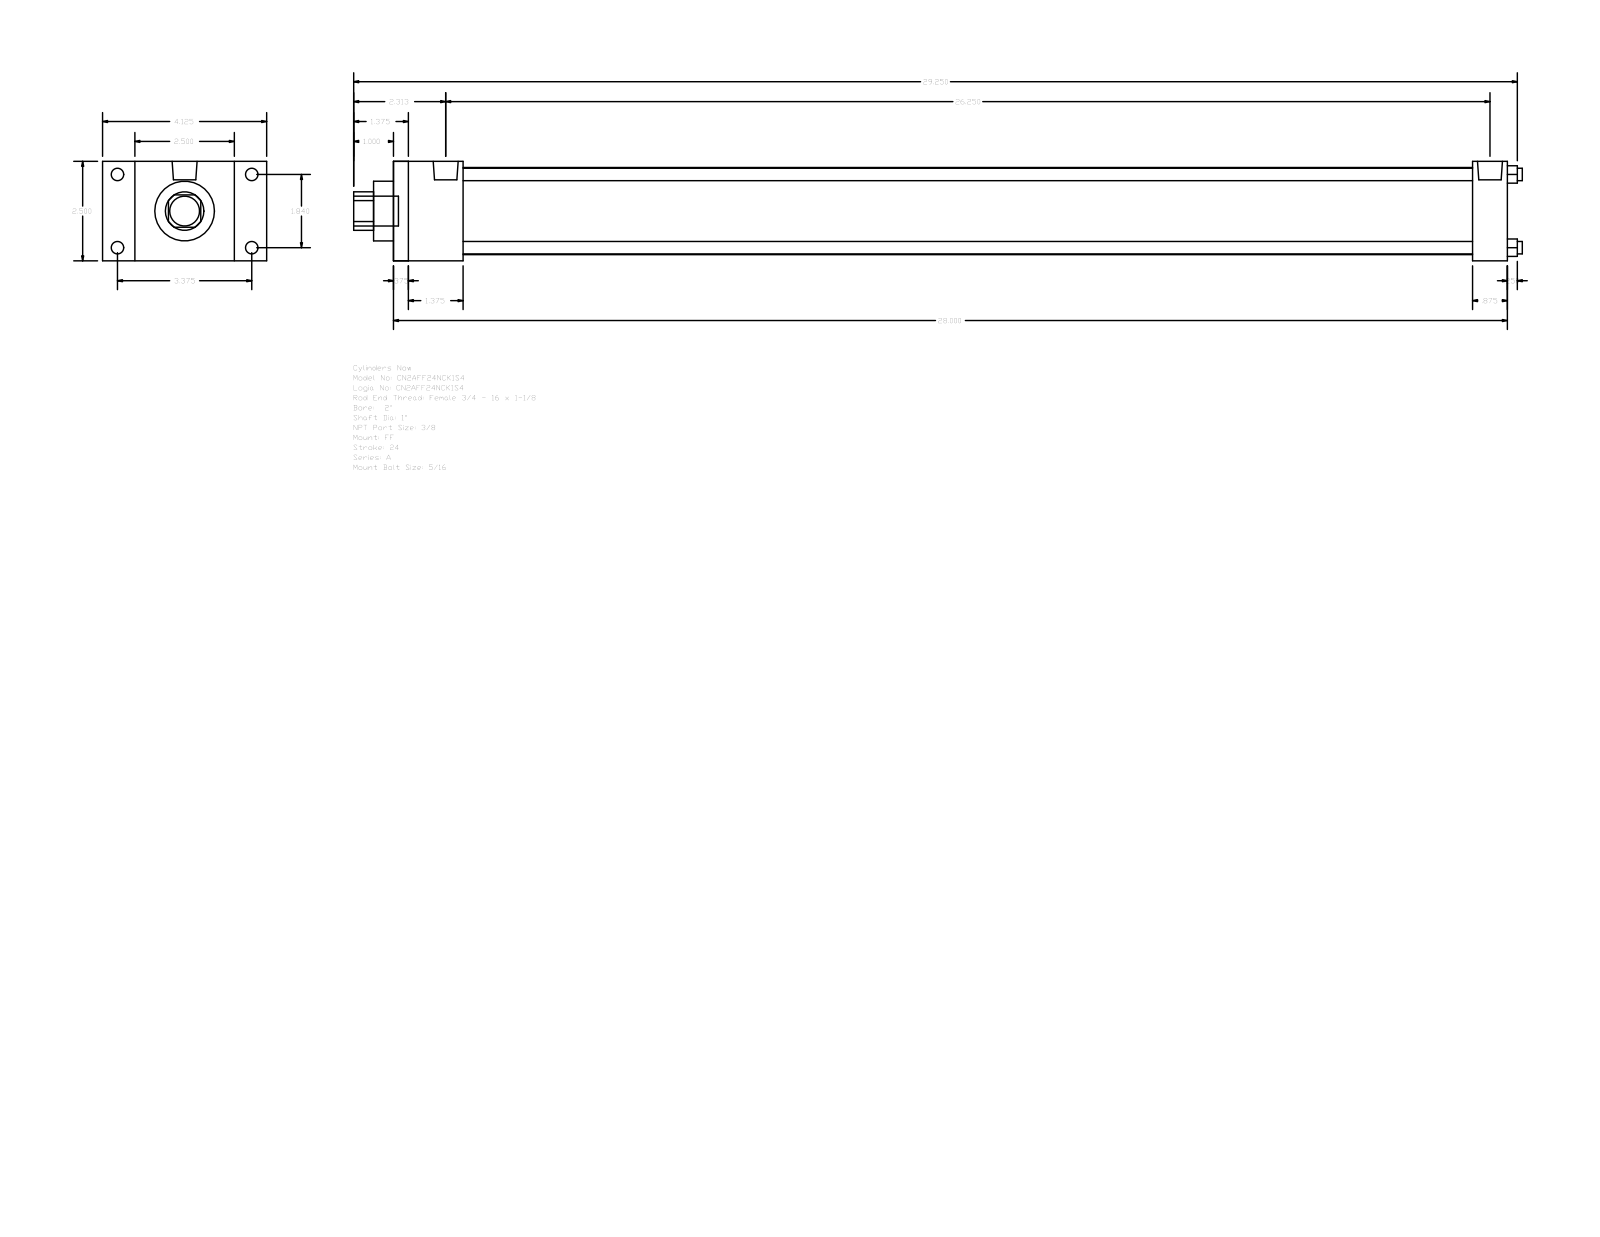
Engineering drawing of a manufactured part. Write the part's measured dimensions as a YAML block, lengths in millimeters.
part_name: "A_FF__0200_1"
step_written_by: "GSSL Pune (CONFIG_CONTROL_DESIGN)"
units: millimeters
bodies: {solids: 0, faces: 92, planar: 64, cylindrical: 28, other: 0}
overall_size: [746.12, 104.78, 63.5]
round_holes:
  - {diameter: 7.94, count: 4}
  - {diameter: 25.4, count: 1}
  - {diameter: 38.1, count: 1}
  - {diameter: 55.63, count: 1}
round_bosses_or_shafts:
  - {diameter: 7.94, count: 4}
  - {diameter: 5.56, count: 4}
  - {diameter: 15.93, count: 2}
  - {diameter: 19.05, count: 1}
partial_cylinders:
  - {radius: 12.29, count: 1}
face_to_face_distances: [63.5, 711.2, 701.68, 9.52, 22.22, 20.64, 44.45, 688.98, 34.93, 679.46]
hole_center_spacings: [33.05, 46.74, 66.1]
